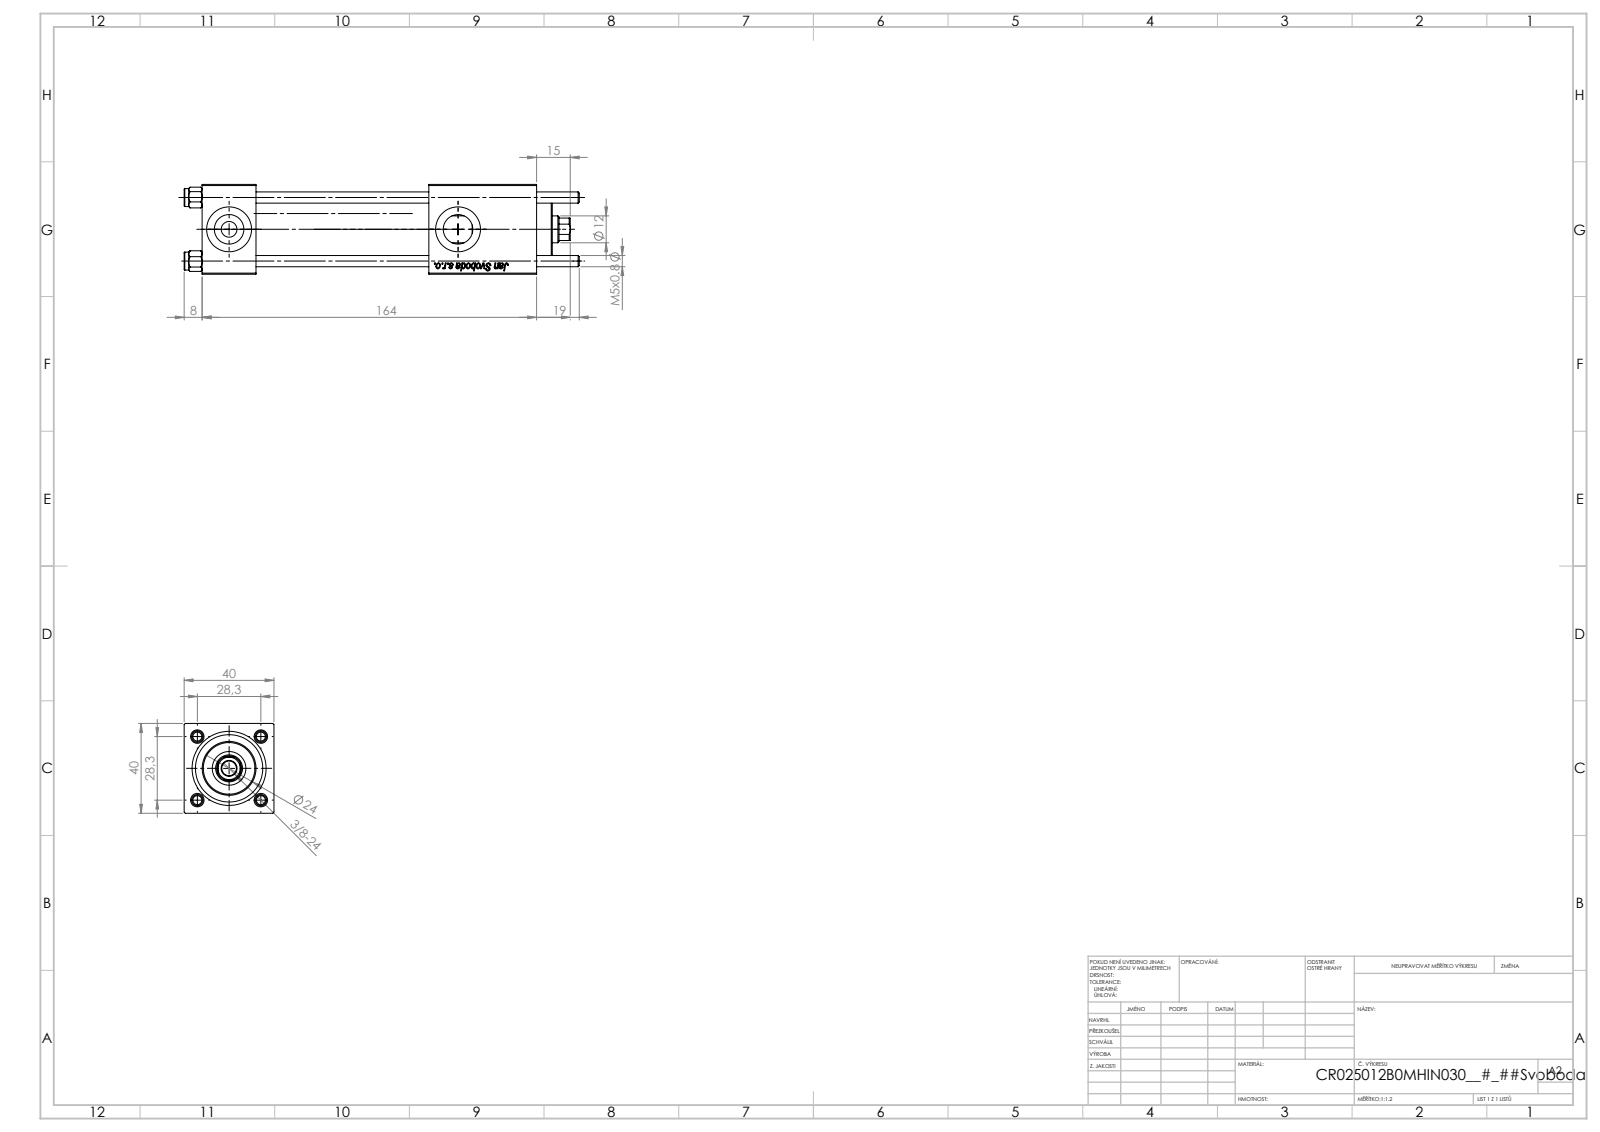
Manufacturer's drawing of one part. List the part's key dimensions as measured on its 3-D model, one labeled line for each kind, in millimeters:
Part name (STEP PRODUCT): V215_VC_A; NUT_M5_B; V215CR_B_TYCINKA; V215CR_VCP_B (+1 more)
STEP written by: SolidWorks 2019 (CONFIG_CONTROL_DESIGN)
Units: millimetres
Bodies: 11 solids, 1155 faces (429 planar, 78 cylindrical, 648 other)
Overall size (bounding box): 176 × 40 × 40
Volume: 158 550 mm³ · Surface area: 66 913 mm²
Round holes (diameter × count): ⌀5 ×4, ⌀20 ×3, ⌀7 ×2, ⌀13.16 ×2, ⌀6.5 ×1, ⌀12 ×1, ⌀15 ×1, ⌀25 ×1, ⌀30 ×1
Round bosses / shafts (diameter × count): ⌀8 ×4, ⌀31 ×1, ⌀24 ×1
Partial cylindrical surfaces — rounded edges, fillets, slot ends (radius × count): R5.5 ×1
Main face-to-face distances: 40, 24, 120.3, 96.3, 101, 77, 19.3, 149, 125, 48
Hole centre spacings: 20.01, 28.3, 40.02, 102
